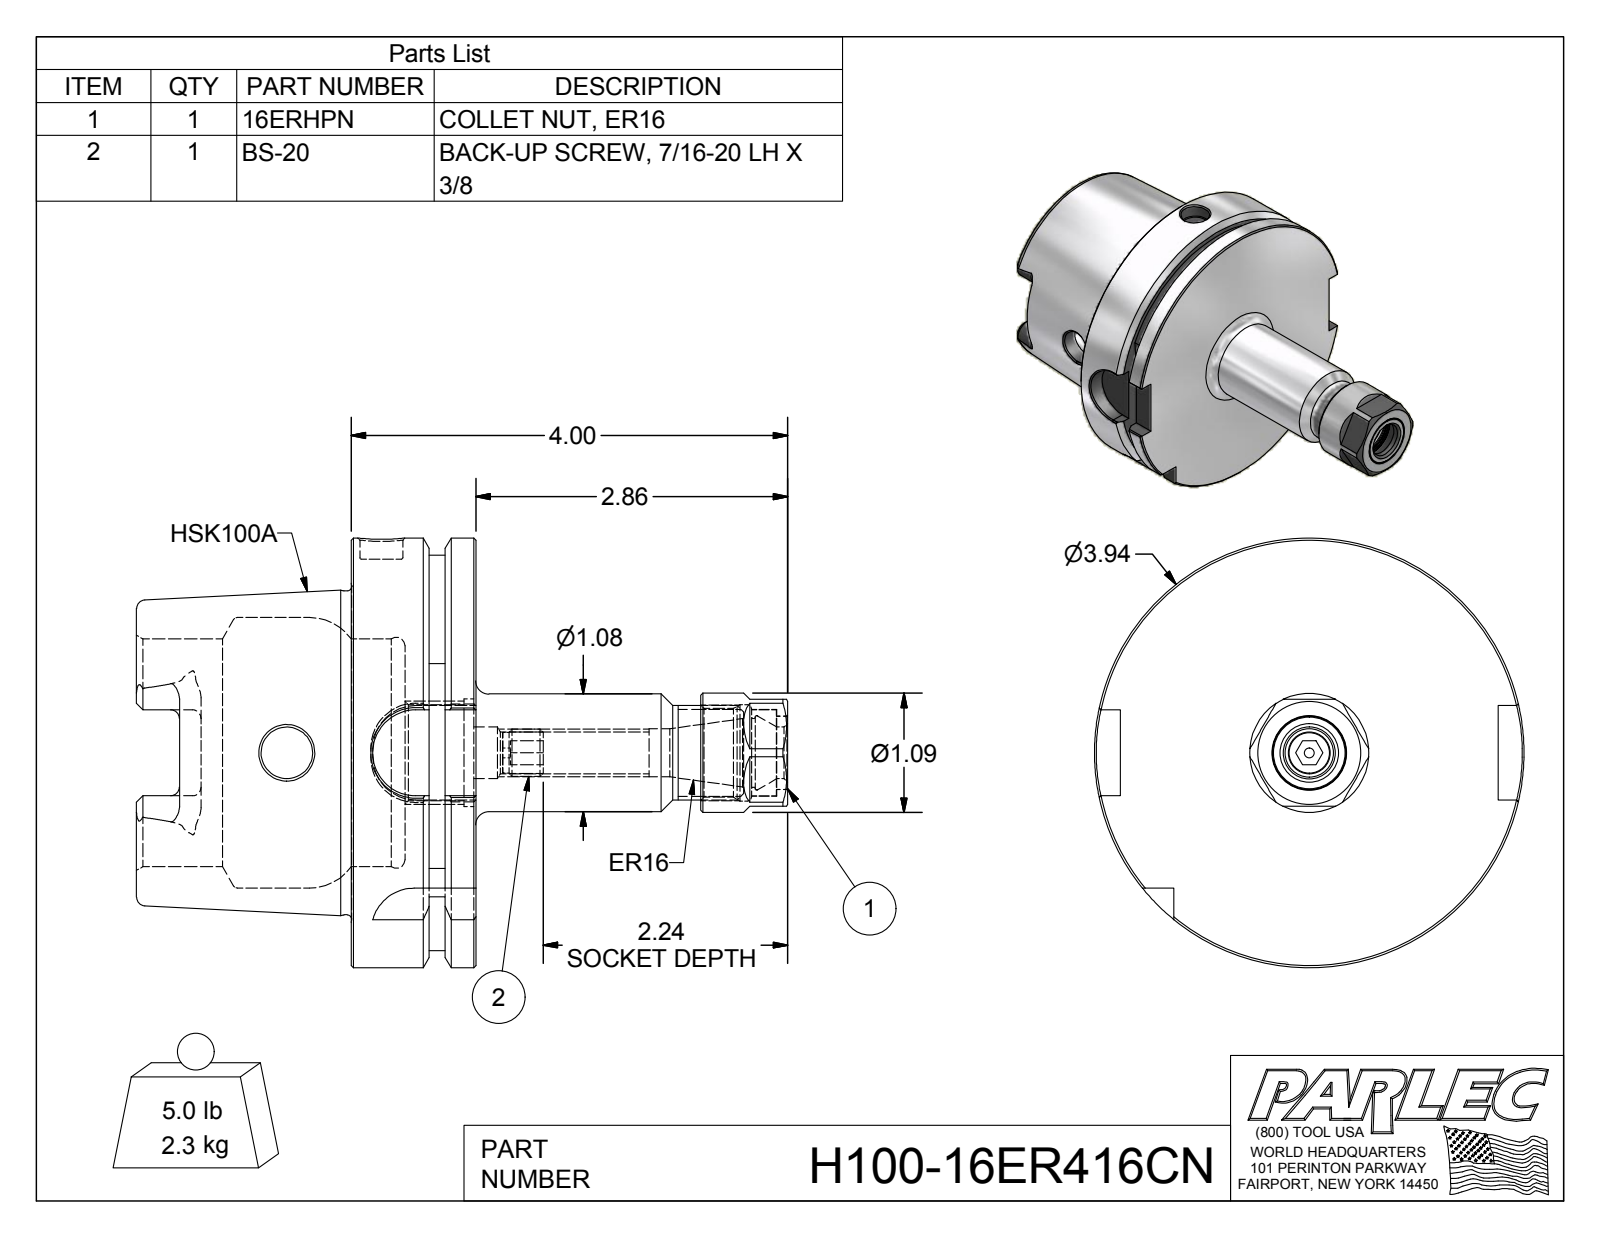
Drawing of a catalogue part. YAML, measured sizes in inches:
part_name: "H100-16ER416CN; H100-16ER4-1; BS-20; 16ERHPN"
step_written_by: "Autodesk Inventor 2012 (AUTOMOTIVE_DESIGN)"
units: inches
bodies: {solids: 4, faces: 188, planar: 73, cylindrical: 49, other: 66}
overall_size: [5.969, 3.937, 3.937]
volume: 17.53
surface_area: 96.57
round_holes:
  - {diameter: 0.472, count: 2}
  - {diameter: 0.09, count: 1}
  - {diameter: 0.383, count: 1}
  - {diameter: 0.394, count: 1}
  - {diameter: 0.44, count: 1}
  - {diameter: 0.472, count: 1}
  - {diameter: 0.474, count: 1}
  - {diameter: 0.63, count: 1}
  - {diameter: 0.674, count: 1}
  - {diameter: 0.68, count: 1}
  - {diameter: 0.794, count: 1}
  - {diameter: 0.814, count: 1}
round_bosses_or_shafts:
  - {diameter: 3.937, count: 1}
  - {diameter: 2.967, count: 1}
  - {diameter: 1.092, count: 1}
  - {diameter: 1.08, count: 1}
  - {diameter: 0.866, count: 1}
  - {diameter: 0.79, count: 1}
  - {diameter: 0.67, count: 1}
  - {diameter: 0.432, count: 1}
partial_cylinders:
  - {radius: 0.079, count: 6}
  - {radius: 0.192, count: 4}
  - {radius: 0.394, count: 4}
  - {radius: 1.811, count: 1}
face_to_face_distances: [1.142, 0.492, 0.65, 1.969, 2.461, 3.11, 2.83, 0.861, 0.369, 0.28]
